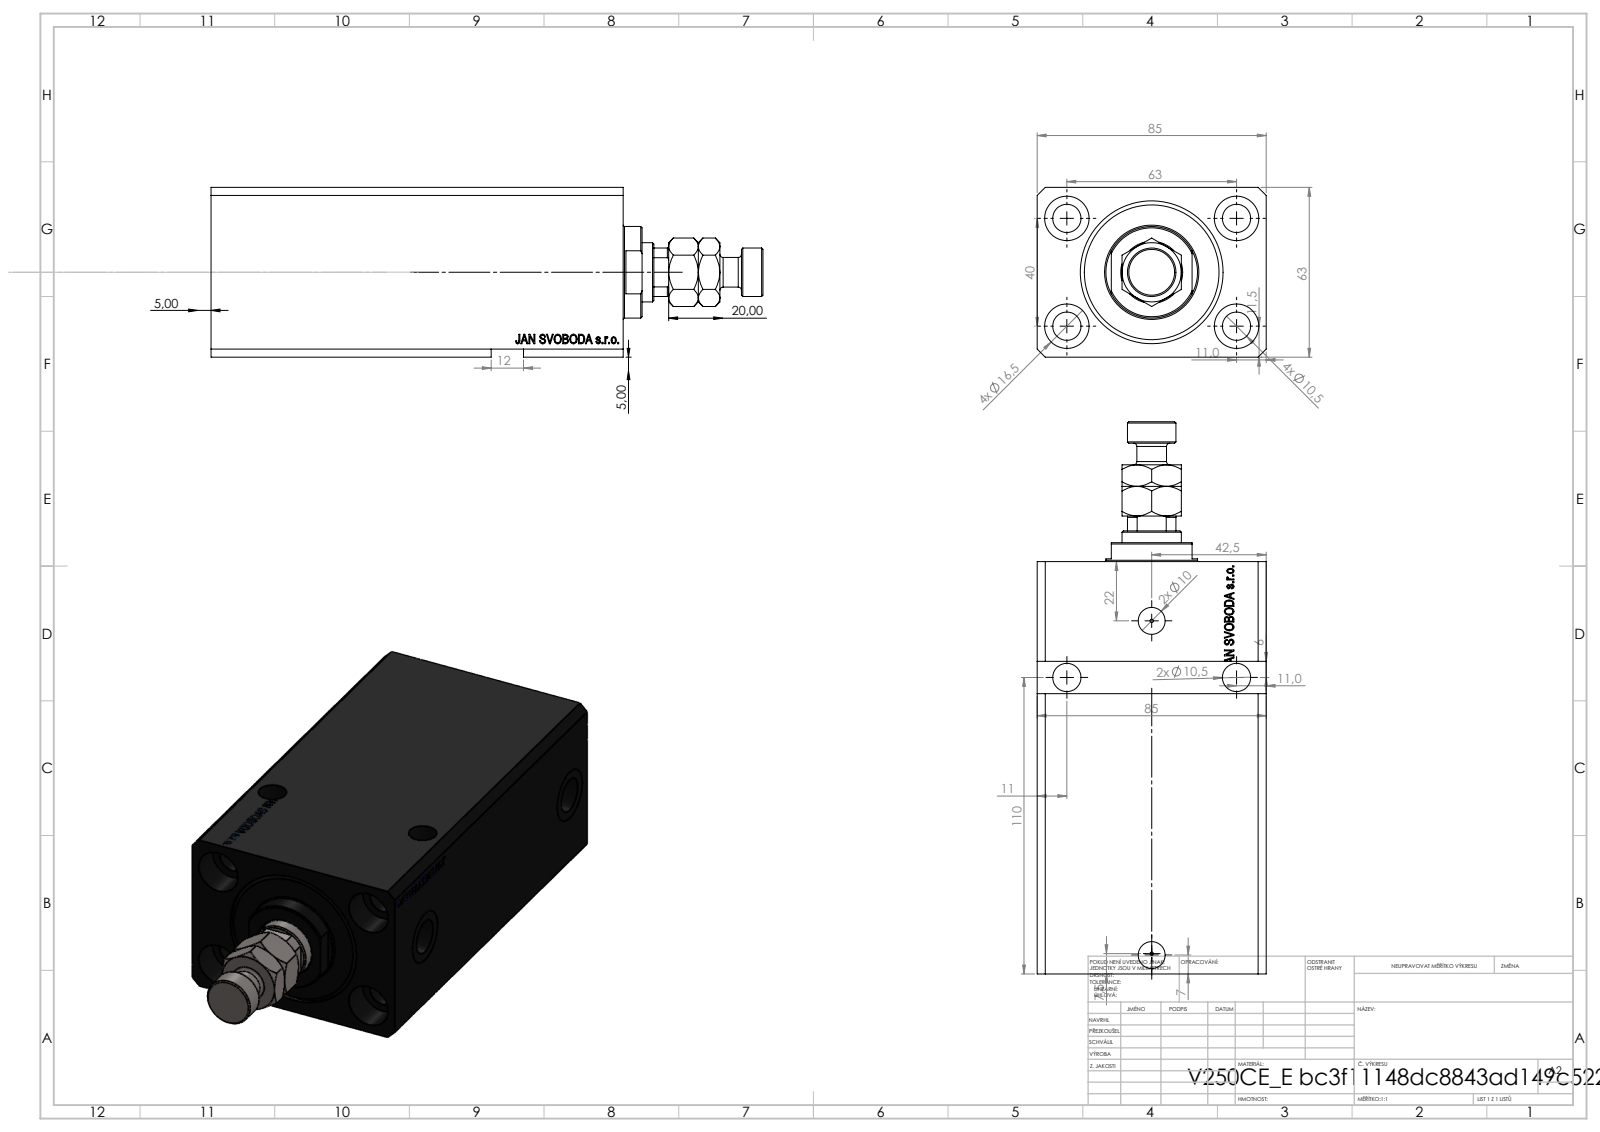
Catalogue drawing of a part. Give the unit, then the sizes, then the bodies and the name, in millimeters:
Units: millimetres
Overall size (bounding box): 205 × 85 × 63
Round holes (diameter × count): ⌀10.5 ×8, ⌀1.25 ×4, ⌀16.5 ×4, ⌀10 ×2, ⌀13.16 ×2, ⌀20 ×2, ⌀12.5 ×1, ⌀22 ×1, ⌀40 ×1, ⌀53 ×1
Round bosses / shafts (diameter × count): ⌀34 ×1, ⌀18 ×1, ⌀11 ×1
Partial cylindrical surfaces — rounded edges, fillets, slot ends (radius × count): R10.5 ×1
Main face-to-face distances: 63, 85, 17, 153, 136, 11.4, 124.6, 141.6, 56, 60
Hole centre spacings: 37.31, 63, 37.86, 40, 41.8, 42.15, 74.63, 75
Volume: 676 886 mm³ · Surface area: 129 466 mm²
Bodies: 4 solids, 989 faces (475 planar, 108 cylindrical, 406 other)
Part name (STEP PRODUCT): V250CE_VC_E; V250CE_C_VCP; MFA; V250CE_E_Body
STEP written by: SolidWorks 2019 (CONFIG_CONTROL_DESIGN)
